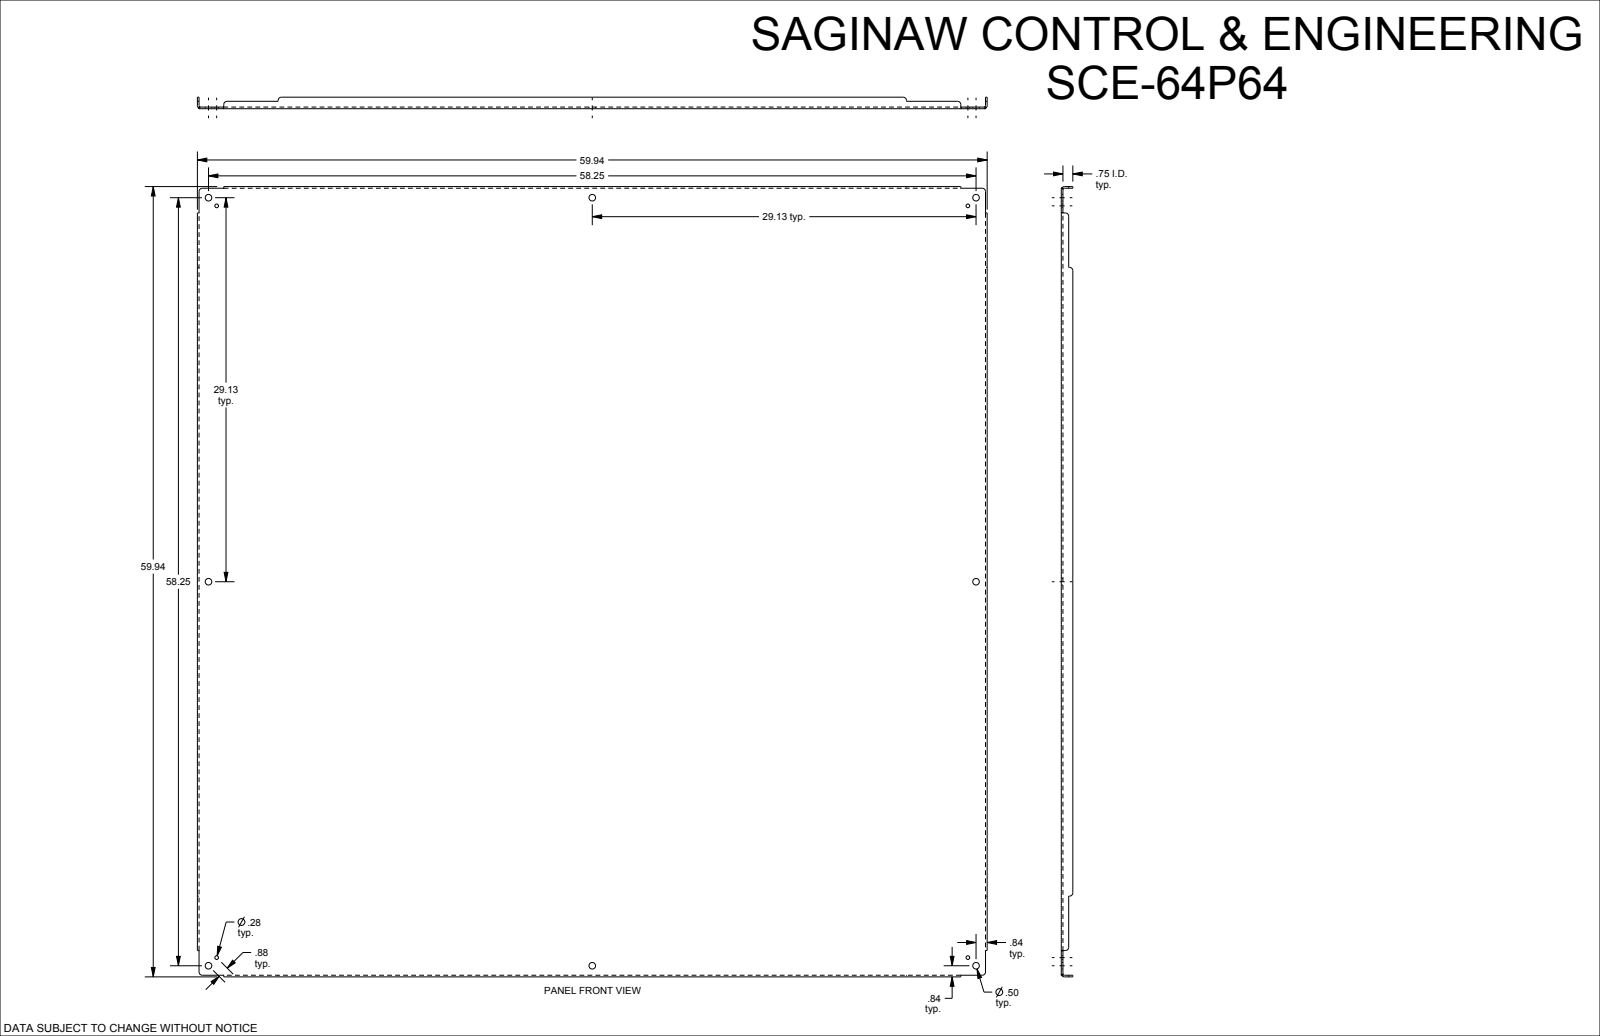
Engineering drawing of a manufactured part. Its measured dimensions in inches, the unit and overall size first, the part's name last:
Units: inches
Overall size (bounding box): 59.938 × 59.938 × 0.875
Round holes (diameter × count): ⌀0.5 ×8, ⌀0.281 ×4
Partial cylindrical surfaces — rounded edges, fillets, slot ends (radius × count): R0.25 ×12, R0.112 ×4, R0.237 ×4
Main face-to-face distances: 0.125, 0.125, 59.813, 59.687, 59.938, 0.75, 0.875, 0.312, 0.438, 0.563
Hole centre spacings: 28.513, 29.125, 57.634, 64.296, 65.125, 58.25, 0.875, 41.189
Volume: 466.2 in³ · Surface area: 7 491 in²
Bodies: 1 solid, 110 faces (46 planar, 40 cylindrical, 24 other)
Part name (STEP PRODUCT): SCE-64P64
STEP written by: SolidWorks 2019 (CONFIG_CONTROL_DESIGN)
